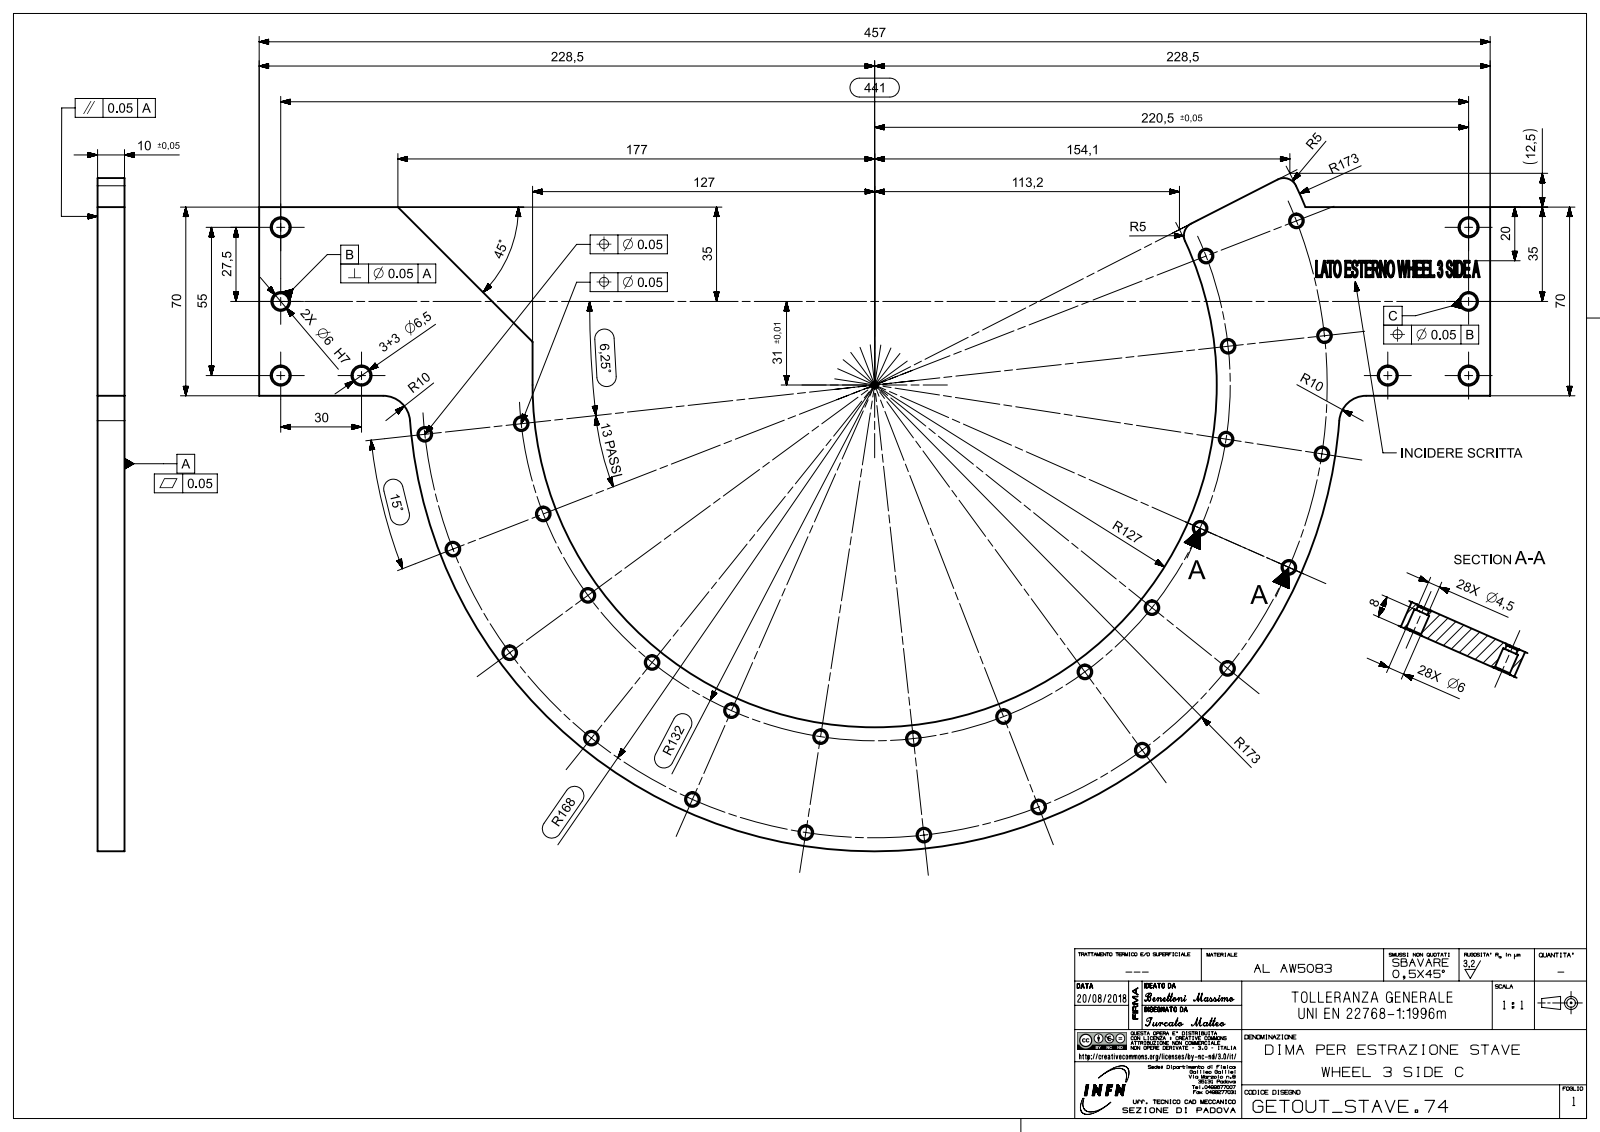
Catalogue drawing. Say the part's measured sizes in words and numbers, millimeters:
The part is named "bezA730AE56ccvu". Its 3-D file was written by "SIEMENS PLM Software NX 12.0 (AUTOMOTIVE_DESIGN)". It is 1 solid with 403 faces: 222 planar, 71 cylindrical and 110 other. Overall it measures 457 by 249.78 by 10 millimeters. Its volume is 337 967 cubic millimeters and its surface area 89 618 square millimeters. Round holes: 30 of diameter 6, 28 of diameter 4.5, 6 of diameter 6.5. Partial cylindrical surfaces (rounded edges, fillets, slot ends): 2 of radius 5, 2 of radius 10, 1 of radius 127, 1 of radius 173. The main face-to-face distances are 10, 70, 457, 8, 2, 355.5, 101.5, 9.7, 1.7, 5.38. The hole center spacings are 52.98, 85.08, 34.46, 68.33, 153.21, 119.52, 119.53, 184.85.
